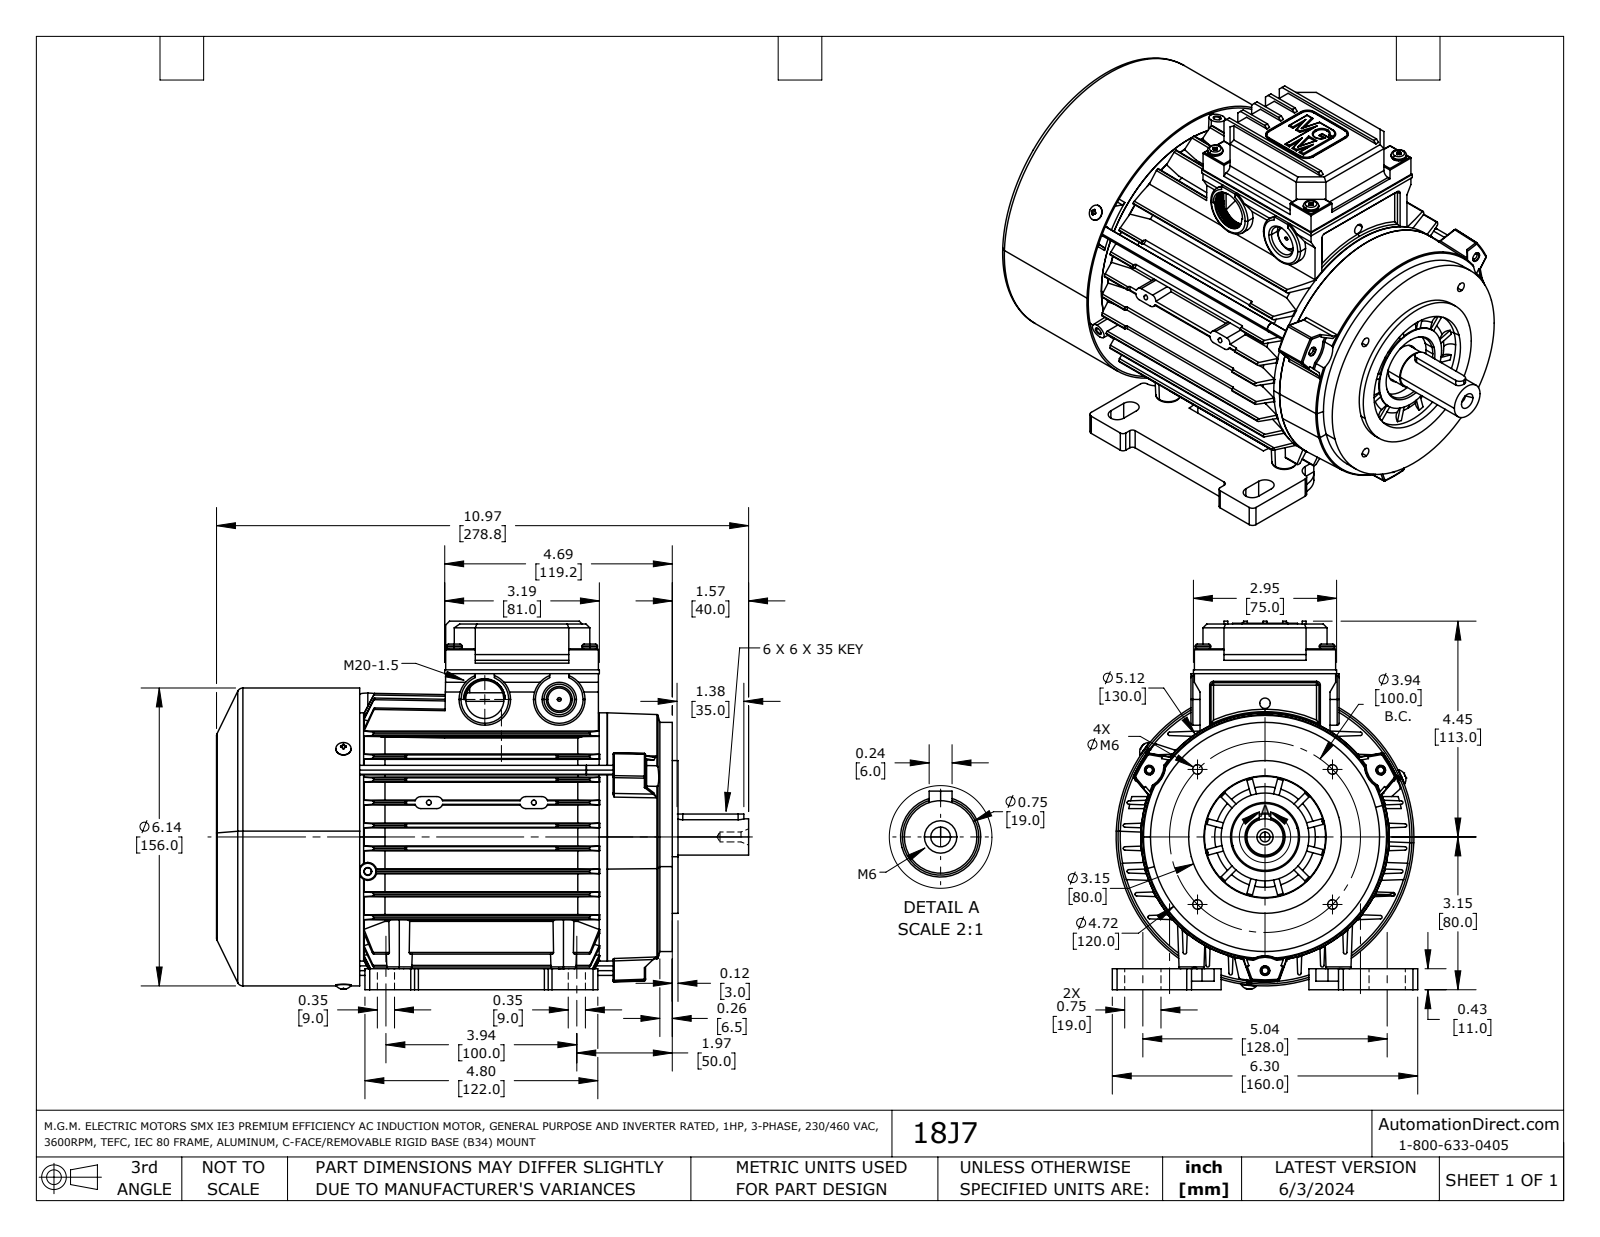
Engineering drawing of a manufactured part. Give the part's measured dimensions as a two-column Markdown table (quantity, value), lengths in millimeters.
| quantity | value |
| --- | --- |
| part name | 18J7 |
| STEP written by | SolidWorks 2021 (AUTOMOTIVE_DESIGN) |
| units | millimeters |
| bodies | 27 solids, 3538 faces (1123 planar, 1508 cylindrical, 907 other) |
| overall size | 278.7 × 193 × 160 |
| volume | 840 500 mm³ |
| surface area | 544 600 mm² |
| round holes (diameter × count) | 3 × 12, 3.7 × 8, 5.5 × 8, 4 × 4, 5 × 4, 6 × 4, 6.5 × 4, 10 × 4, 3.2 × 3, 4.5 × 3, 4.6 × 3, 7 × 3 |
| round bosses / shafts (diameter × count) | 3 × 10, 8 × 7, 5 × 7, 9.8 × 4, 3.5 × 4, 27 × 3, 2 × 3, 6.3 × 2 |
| partial cylindrical surfaces (radius × count) | 1 × 260, 0.2 × 56, 0.4 × 36, 0.5 × 30, 0.9 × 30, 0.1 × 16, 0.8 × 16, 2 × 16 |
| main face-to-face distances | 11, 2, 24, 11.8, 47.5, 83.9, 72.2, 71.7, 59.9, 12.2 |
| hole center spacings | 12.1, 70, 14.5, 19, 28, 31, 31, 39.6 |
